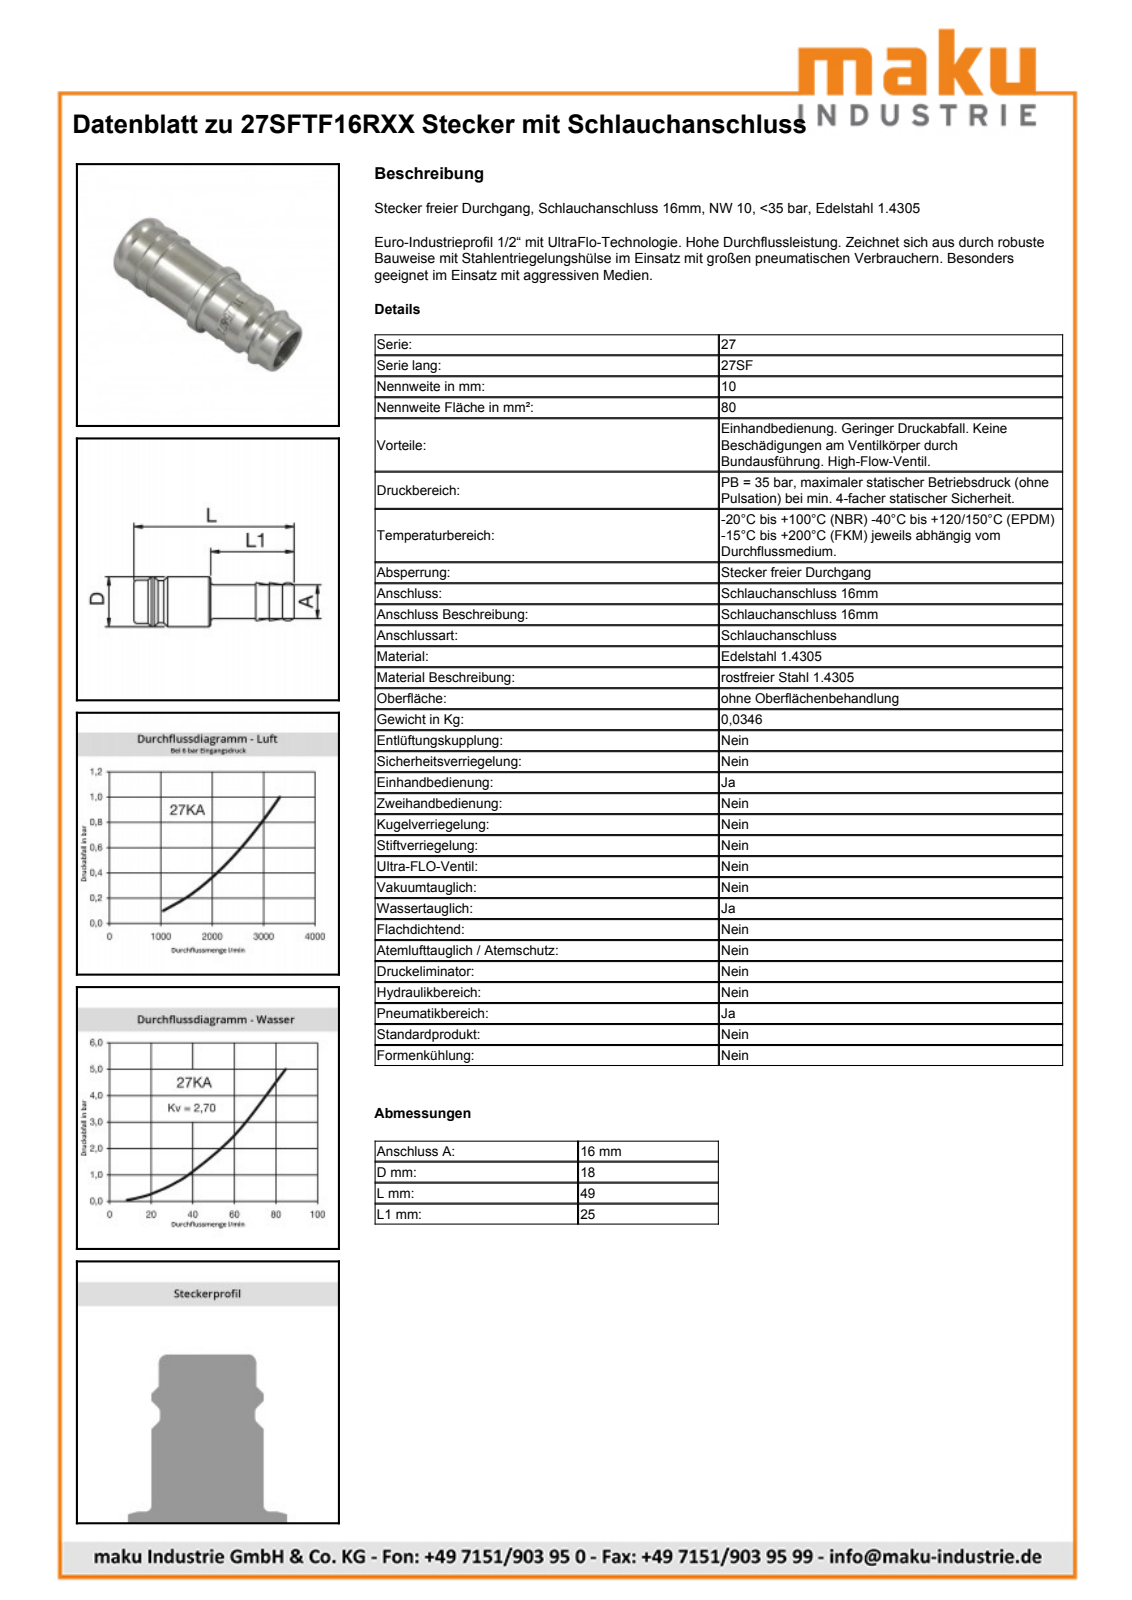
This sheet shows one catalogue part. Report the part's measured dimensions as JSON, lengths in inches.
{"part_name": "D103730", "step_written_by": "Autodesk Inventor 2011 (AUTOMOTIVE_DESIGN)", "units": "inches", "bodies": {"solids": 1, "faces": 28, "planar": 4, "cylindrical": 8, "other": 16}, "overall_size": [1.929, 0.709, 0.709], "volume_in3": 0.271, "surface_area_in2": 6.936, "round_holes": [[0.394, 1], [0.496, 1]], "round_bosses_or_shafts": [[0.709, 1], [0.634, 1], [0.591, 1], [0.512, 1], [0.498, 1]], "face_to_face_distances": [1.083, 0.846, 1.929, 1.476, 0.63, 0.453]}
